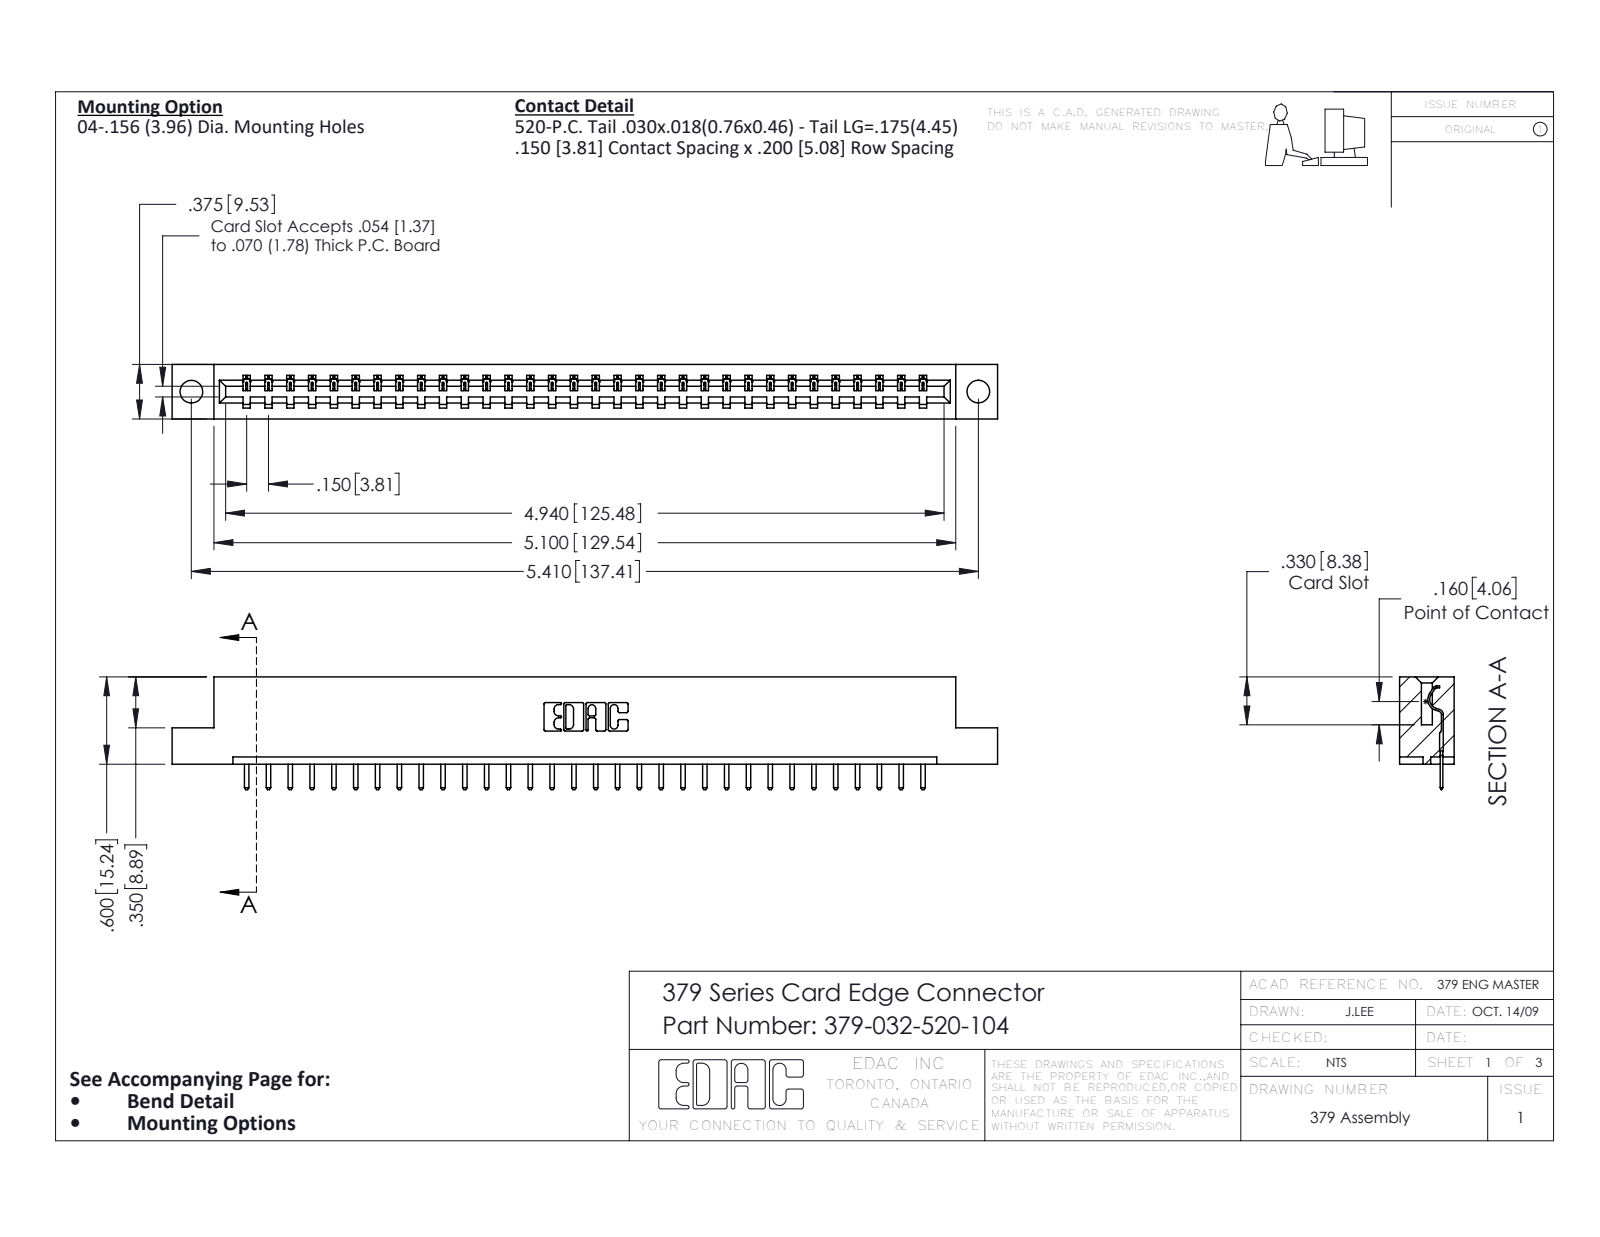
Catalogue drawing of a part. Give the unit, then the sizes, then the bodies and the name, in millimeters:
Units: millimetres
Overall size (bounding box): 144.1 × 19.7 × 9.5
Round holes (diameter × count): ⌀4 ×2
Partial cylindrical surfaces — rounded edges, fillets, slot ends (radius × count): R0.3 ×66, R0.2 ×64, R0.3 ×22, R0.2 ×6, R0.8 ×6, R0.7 ×3, R0.4 ×1, R0.6 ×1
Main face-to-face distances: 7.6, 1.9, 9.5, 5.7, 15.2, 14, 5.1, 3.8, 3.8, 3.8
Hole centre spacings: 137.4
Volume: 14 800 mm³ · Surface area: 14 600 mm²
Bodies: 33 solids, 2098 faces (1478 planar, 620 cylindrical, 0 other)
Part name (STEP PRODUCT): 379-032-520-104; 379 Part_Flush - .156 Dia - TH; 345-292-001_345-293-120
STEP written by: SolidWorks 2016 (CONFIG_CONTROL_DESIGN)
